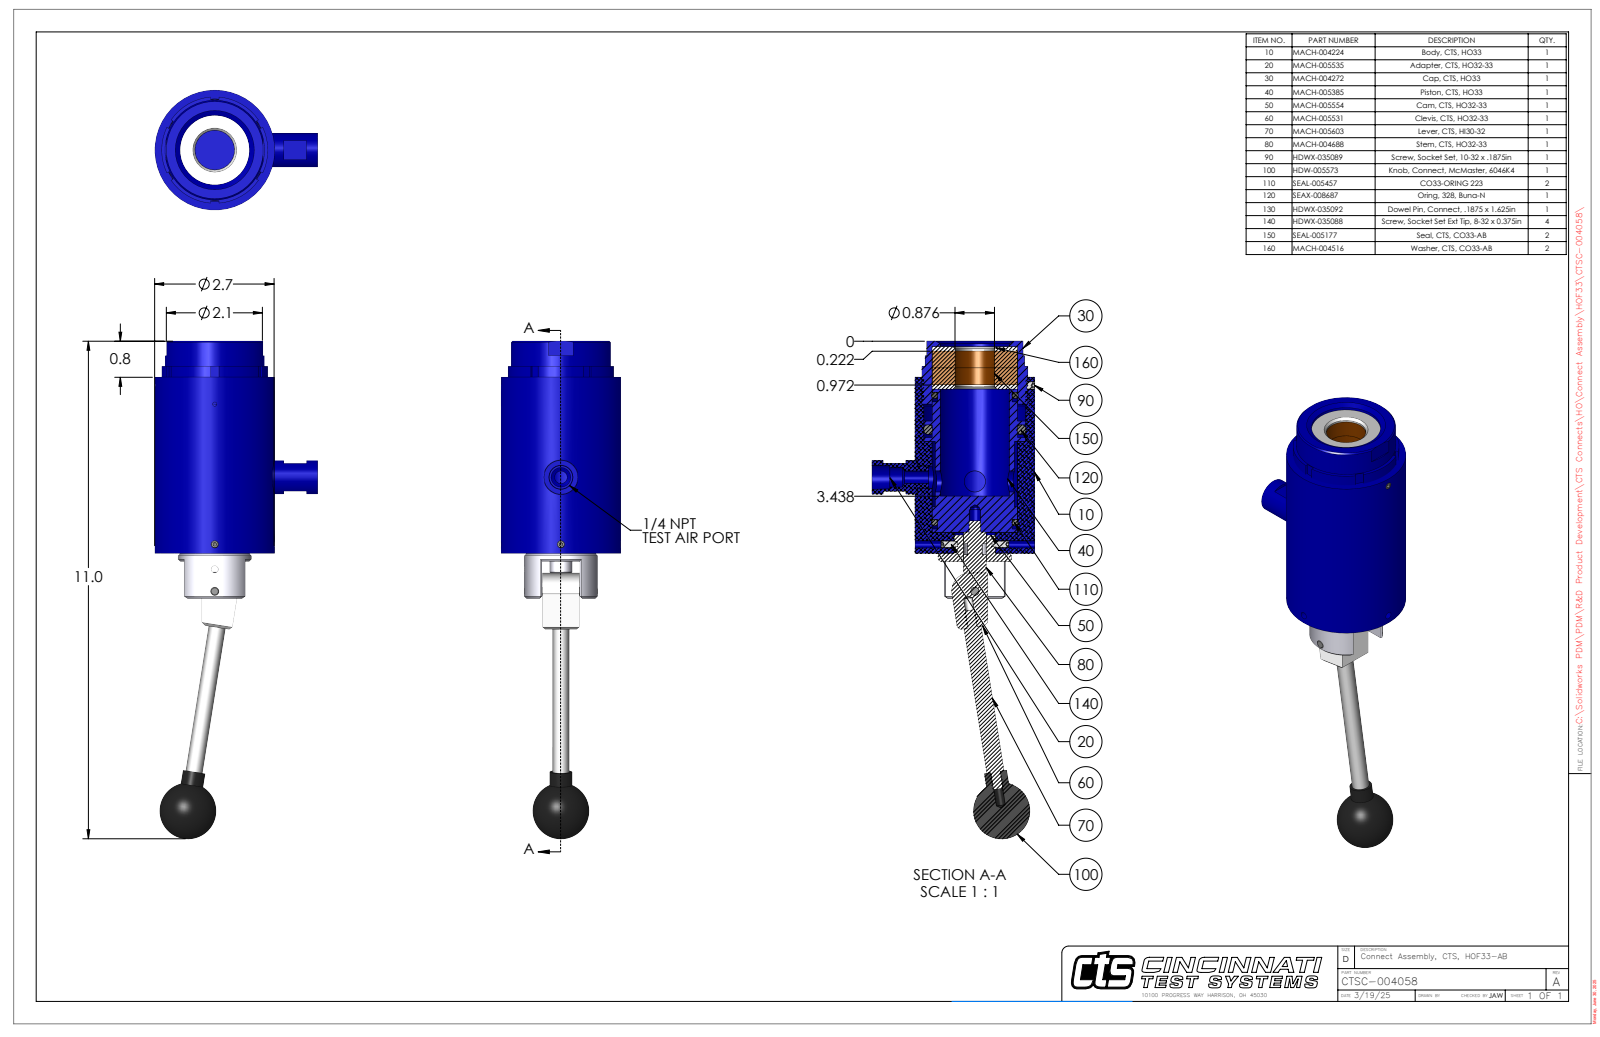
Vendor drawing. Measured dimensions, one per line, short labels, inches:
name: CTSC-004058
written by: SolidWorks 2023 (AUTOMOTIVE_DESIGN)
unit: in
bodies: 14 solids, 546 faces (179 planar, 226 cylindrical, 141 other)
size: 11.035 × 3.6 × 2.65
volume: 22.42 in³; area: 137.5 in²
holes: 3× ⌀0.201, 2× ⌀0.159, 2× ⌀0.469, 1× ⌀0.094, 1× ⌀0.189, 1× ⌀0.19, 1× ⌀0.25, 1× ⌀0.281, 1× ⌀0.438, 1× ⌀0.5, 1× ⌀0.516, 1× ⌀0.524
bosses: 2× ⌀0.75, 2× ⌀0.5, 2× ⌀0.164, 2× ⌀0.109, 1× ⌀2.65, 1× ⌀2.344, 1× ⌀2.2, 1× ⌀1.885
rounds: 1× R0.385, 1× R0.4, 1× R1.13, 1× R1.195
face distances: 0.844, 0.094, 0.75, 0.375, 0.375, 3.736, 4.111, 4.486, 0.469, 3.642
hole spacings: 0.093, 0.488, 1.713, 1.945, 2.033, 2.126, 2.433, 3.658
